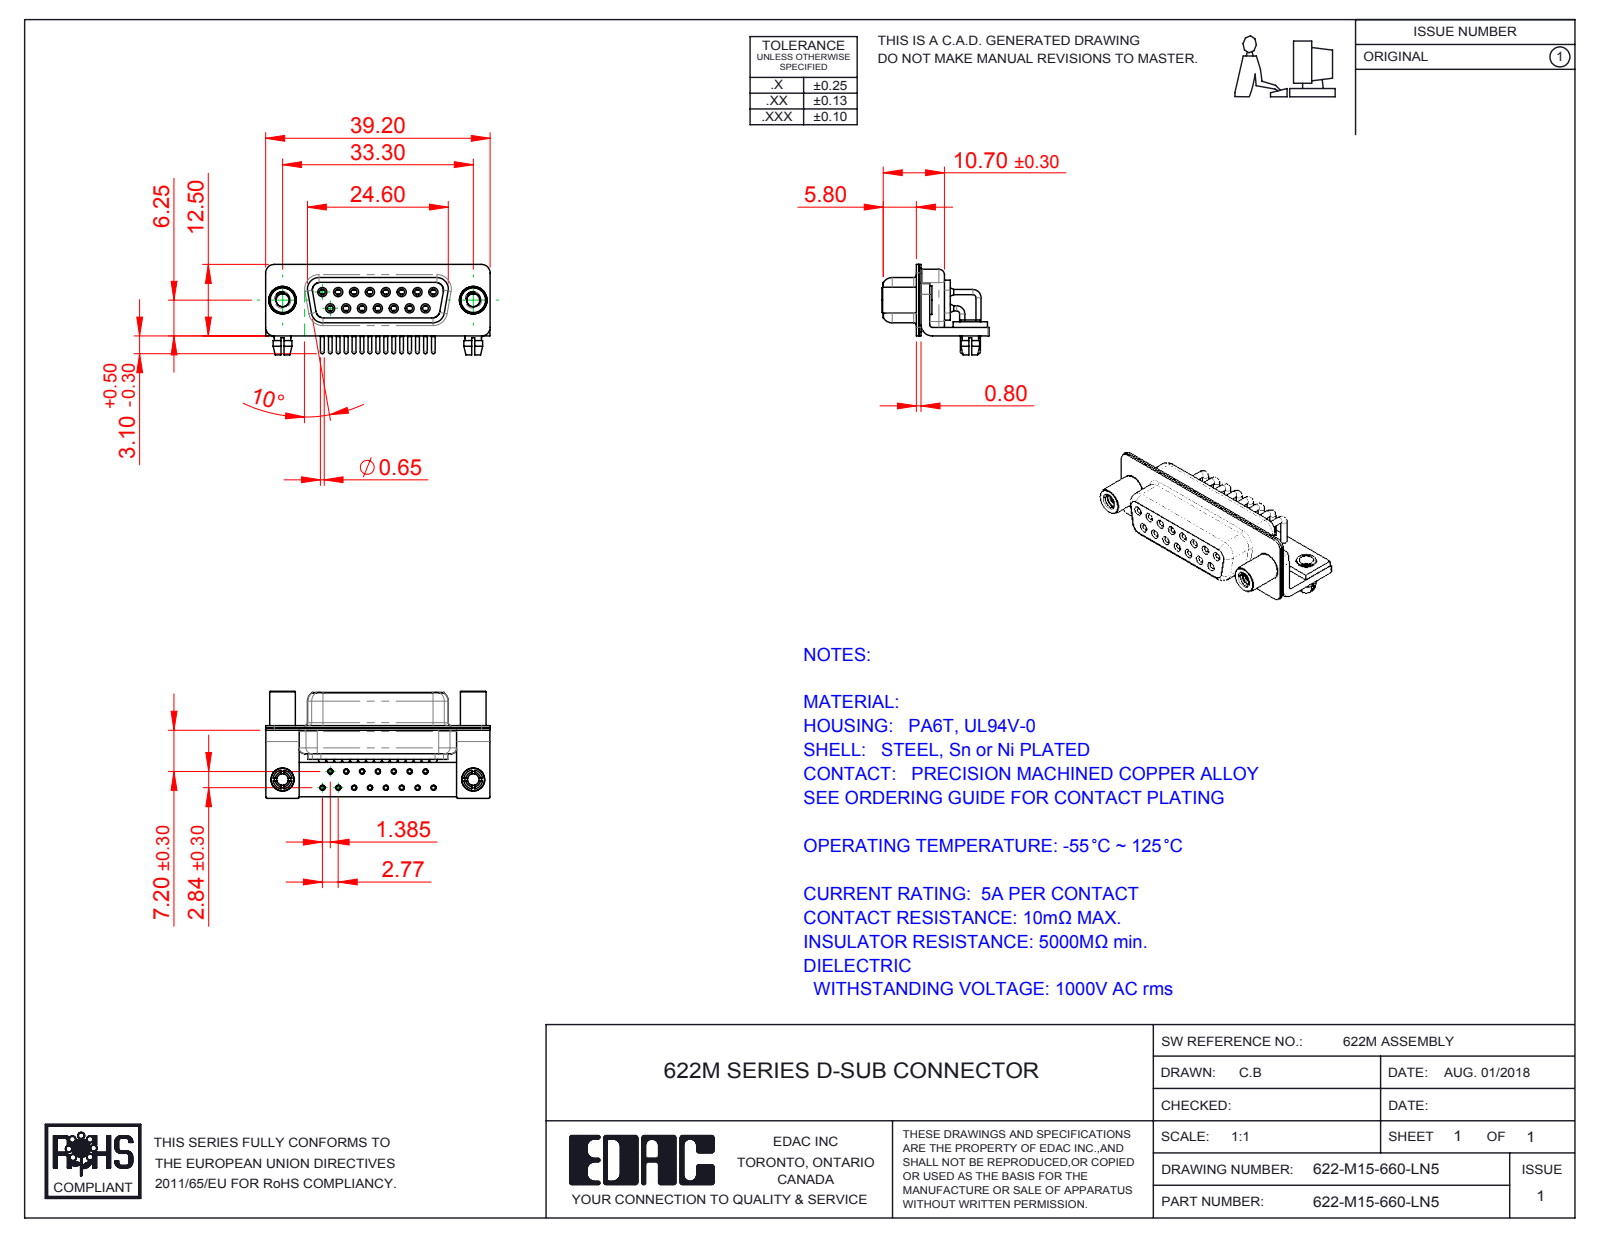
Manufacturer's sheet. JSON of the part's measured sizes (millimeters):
{"part_name": "622M Contact Row 2; 622M Contact Row 1; 622M Shell Rear_15 Contacts; 622M Shell Front_15 Contacts (+6 more)", "step_written_by": "SolidWorks 2016 (CONFIG_CONTROL_DESIGN)", "units": "millimeters", "bodies": {"solids": 25, "faces": 1296, "planar": 368, "cylindrical": 608, "other": 320}, "overall_size": [39.2, 18.7, 15.8], "volume_mm3": 3146, "surface_area_mm2": 8070, "round_holes": [[2, 17], [0.9, 15], [1, 15], [1.1, 15], [1.7, 15], [1.8, 15], [2.26, 2], [2.5, 2], [3.2, 2], [4, 2], [4.8, 2]], "round_bosses_or_shafts": [[0.9, 22], [1.6, 15], [1.5, 15], [0.65, 15], [5, 2], [4.9, 2], [4.5, 2], [4, 2]], "partial_cylinders_radius": [[0.25, 16], [1.5, 16], [2, 13], [1.35, 8], [1.6, 8], [0.5, 5], [0.6, 4], [0.65, 4]], "face_to_face_distances": [0.4, 2.3, 1.9, 0.8, 9.35, 1.5, 1, 1.45, 8.95, 0.85], "hole_center_spacings": [3.16, 2.77, 5.54, 8.31, 11.08, 5.03, 5.04, 7.48]}
